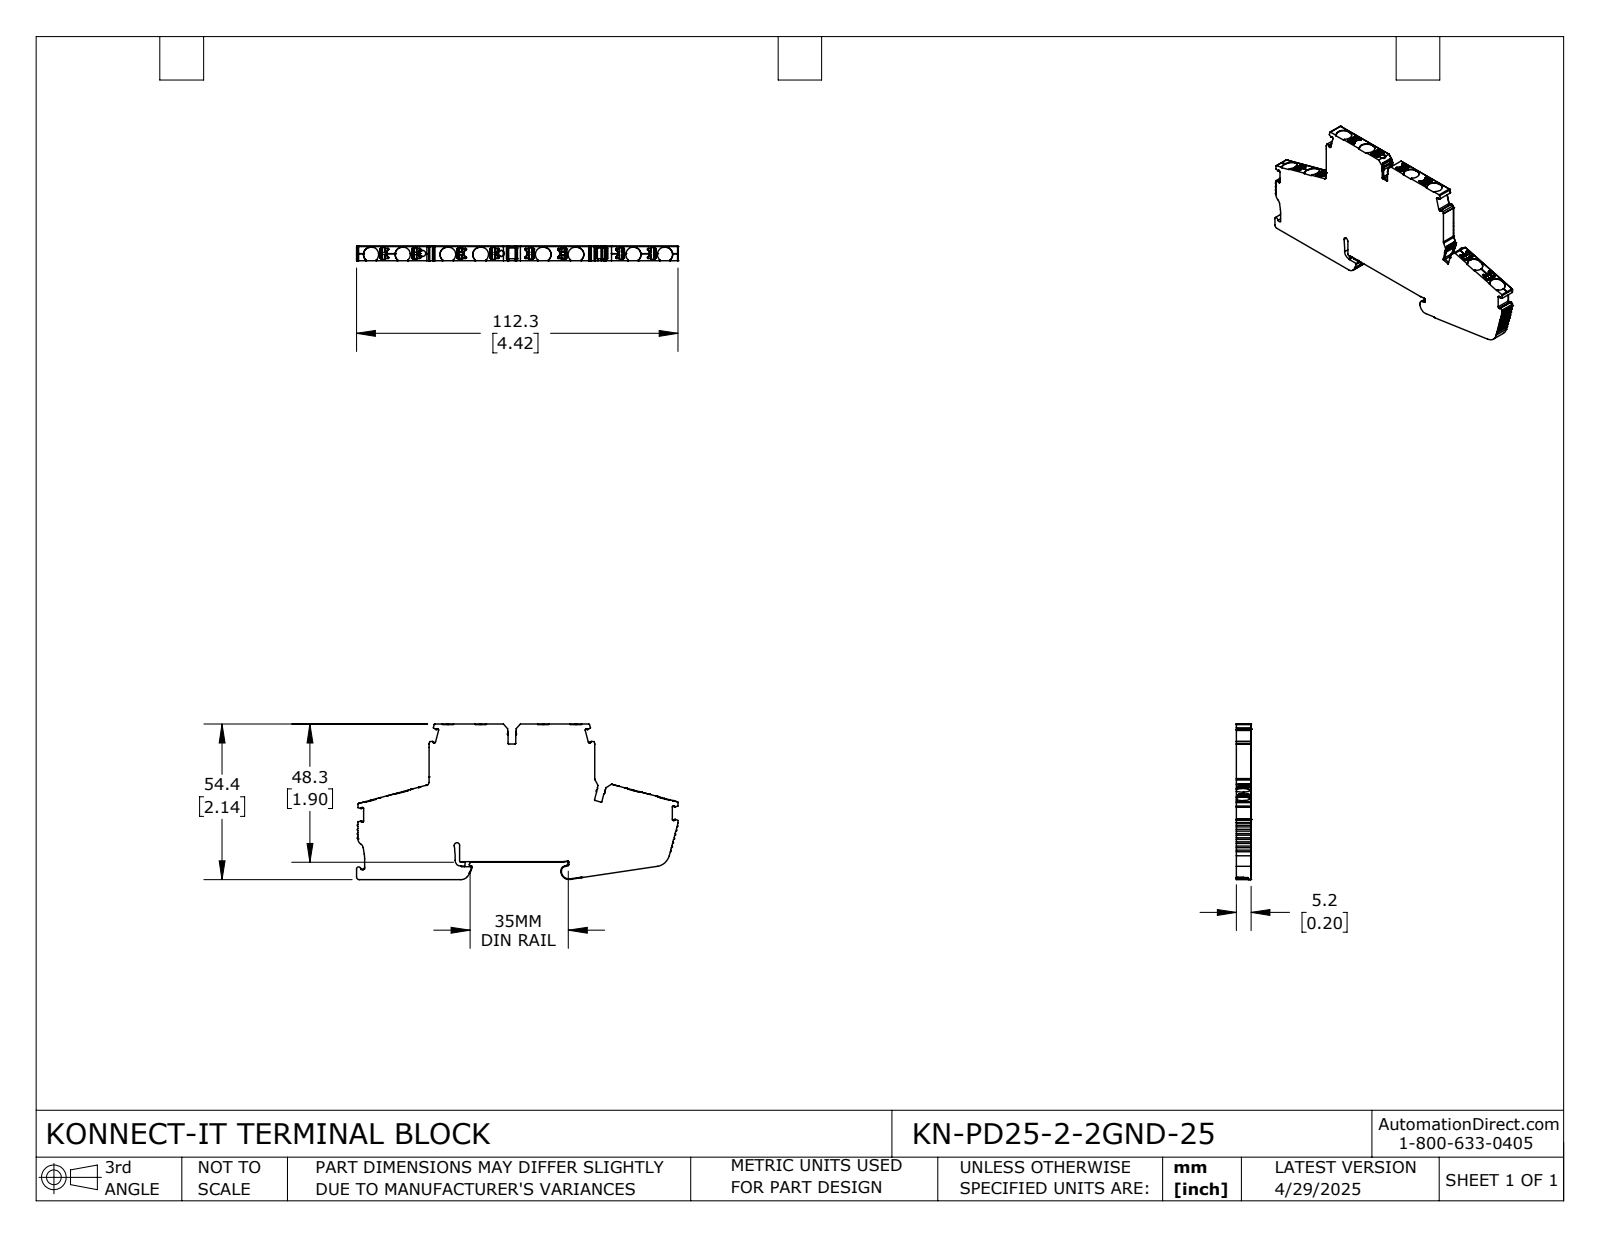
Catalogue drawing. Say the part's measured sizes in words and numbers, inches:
The part is named "KN-PD25-2-2GND-25". Its 3-D file was written by "SolidWorks 2024 (CONFIG_CONTROL_DESIGN)". It is 1 solid with 1151 faces: 562 planar, 451 cylindrical and 138 other. Overall it measures 4.422 by 2.141 by 0.203 inches. Its volume is 1.353 cubic inches and its surface area 16.68 square inches. Round holes: 2 of diameter 0.083. Partial cylindrical surfaces (rounded edges, fillets, slot ends): 97 of radius 0.008, 43 of radius 0.012, 37 of radius 0.004, 32 of radius 0.006, 18 of radius 0.016, 16 of radius 0.1, 15 of radius 0.02, 9 of radius 0.039. The main face-to-face distances are 0.203, 1.893, 2.141, 2.133, 0.24, 1.9, 0.248, 1.885, 2.279, 0.079.
